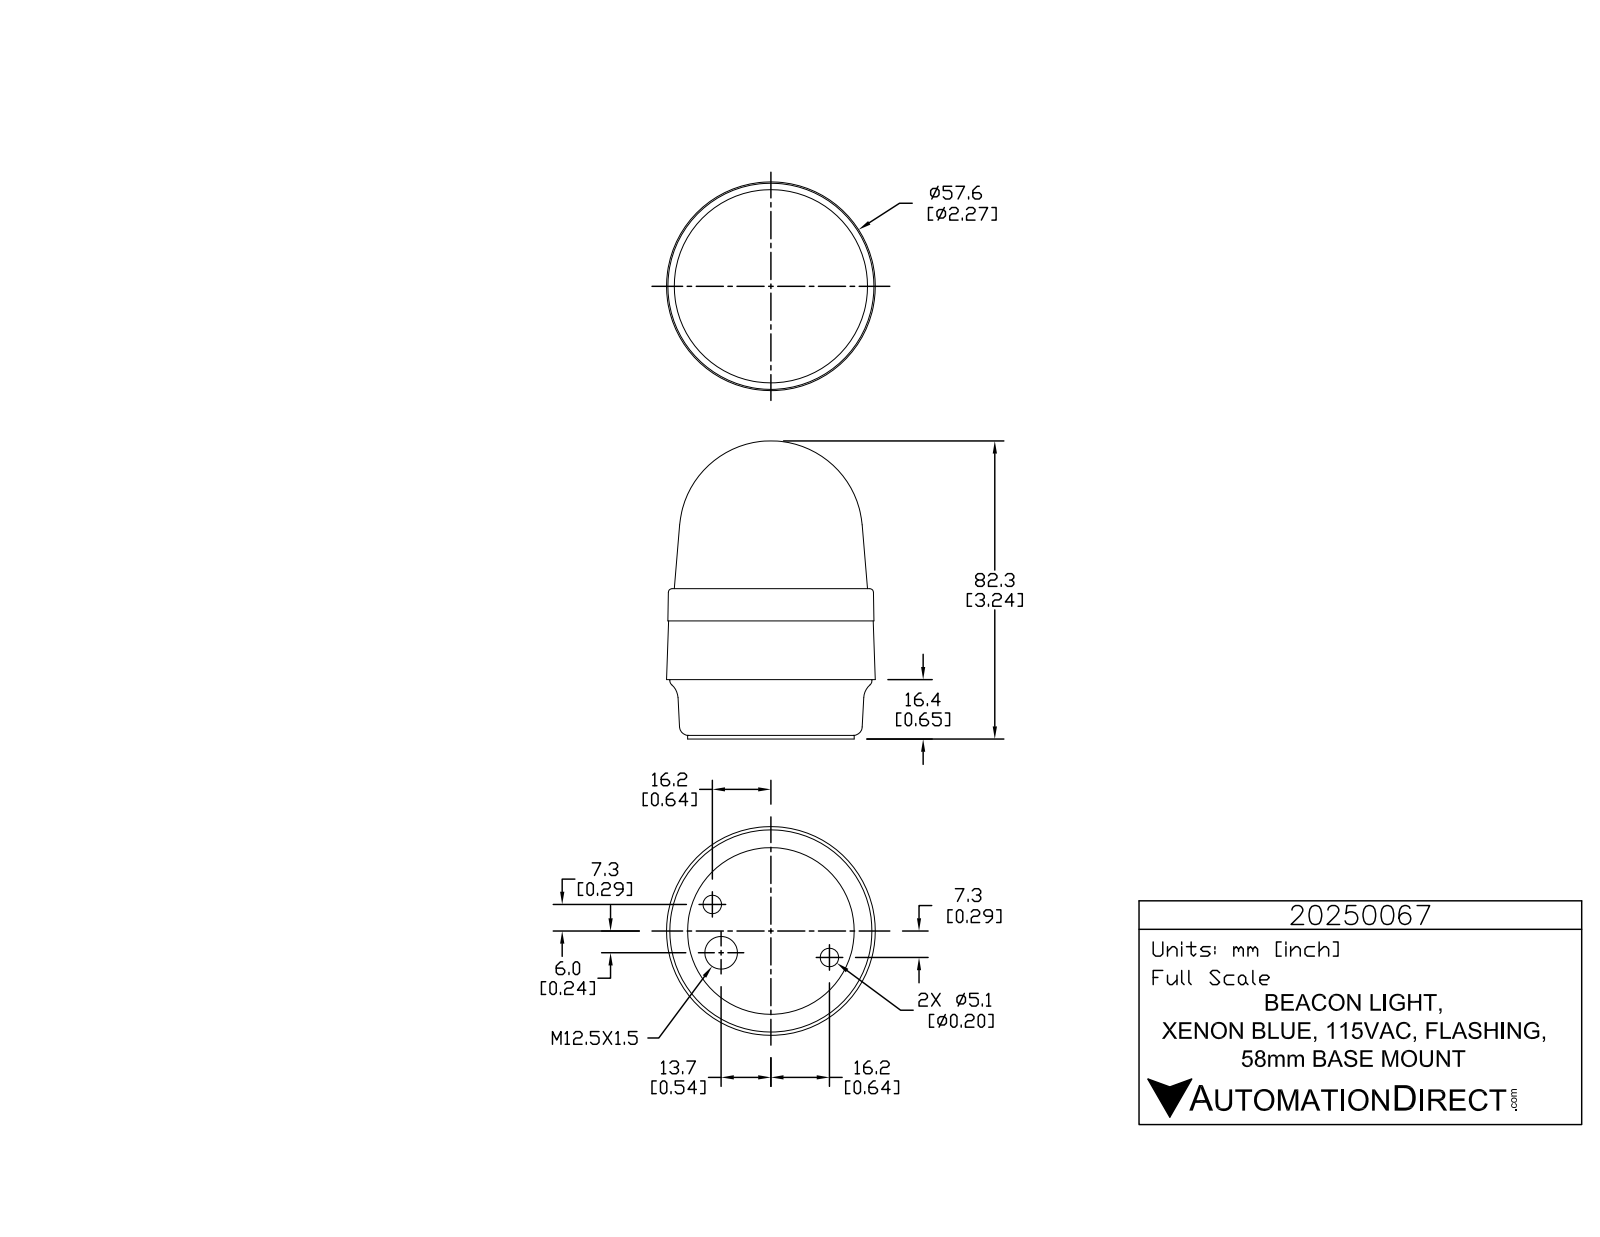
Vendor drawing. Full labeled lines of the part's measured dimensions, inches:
Part name (STEP PRODUCT): 20250067
STEP written by: SolidWorks 2015 (AUTOMOTIVE_DESIGN)
Units: inches
Bodies: 1 solid, 763 faces (527 planar, 145 cylindrical, 91 other)
Overall size (bounding box): 3.24 × 2.269 × 2.269
Volume: 10.03 in³ · Surface area: 25.2 in²
Round holes (diameter × count): ⌀0.039 ×3, ⌀0.201 ×2, ⌀0.354 ×1
Round bosses / shafts (diameter × count): ⌀0.226 ×3, ⌀0.056 ×3, ⌀2.197 ×1, ⌀1.811 ×1
Partial cylindrical surfaces — rounded edges, fillets, slot ends (radius × count): R0.008 ×6, R0.008 ×6, R0.008 ×6, R0.131 ×6, R0.004 ×3, R0.005 ×3, R0.007 ×3, R0.008 ×3
Main face-to-face distances: 0.646, 0.039, 0.606, 1.634, 1.594, 0.988, 1.283, 1.244, 0.638, 0.35
Hole centre spacings: 0.534, 1.179, 1.398
